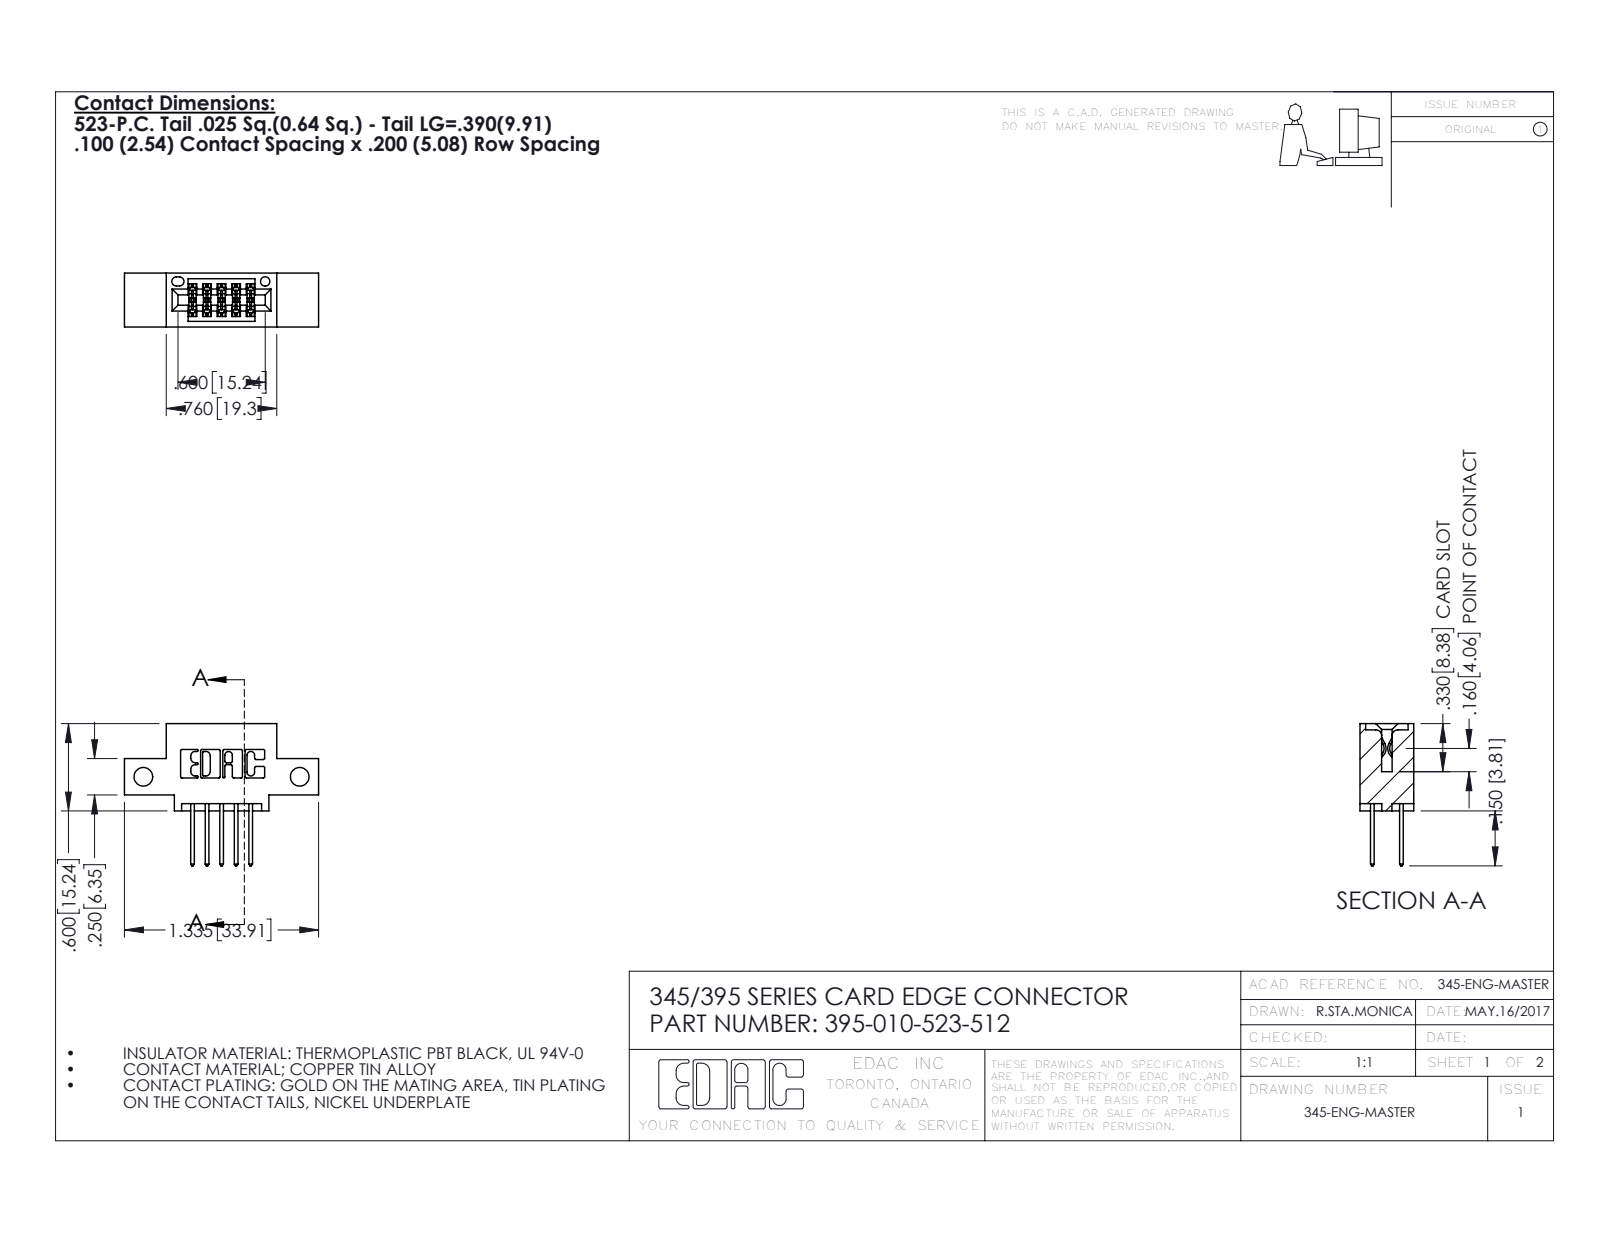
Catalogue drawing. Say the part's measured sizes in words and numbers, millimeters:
The part is named "345-292-001_345-293-123; 345 Part_0.110 Offset - Side Mount; 395-010-523-512". Its 3-D file was written by "SolidWorks 2016 (CONFIG_CONTROL_DESIGN)". It is 11 solids with 630 faces: 414 planar, 216 cylindrical and 0 other. Overall it measures 33.9 by 24.8 by 9.4 millimeters. Its volume is 2 800 cubic millimeters and its surface area 3 486 square millimeters. Round holes: 2 of diameter 3.3, 1 of diameter 1.6. Partial cylindrical surfaces (rounded edges, fillets, slot ends): 22 of radius 0.3, 15 of radius 0.2, 10 of radius 0.3, 6 of radius 0.2, 6 of radius 0.8, 3 of radius 0.7, 2 of radius 0.4, 2 of radius 0.5. The main face-to-face distances are 5.1, 7.6, 1.8, 9.4, 2.5, 2.5, 6.9, 0.6, 6.4, 5.7. The hole center spacings are 27.3.
